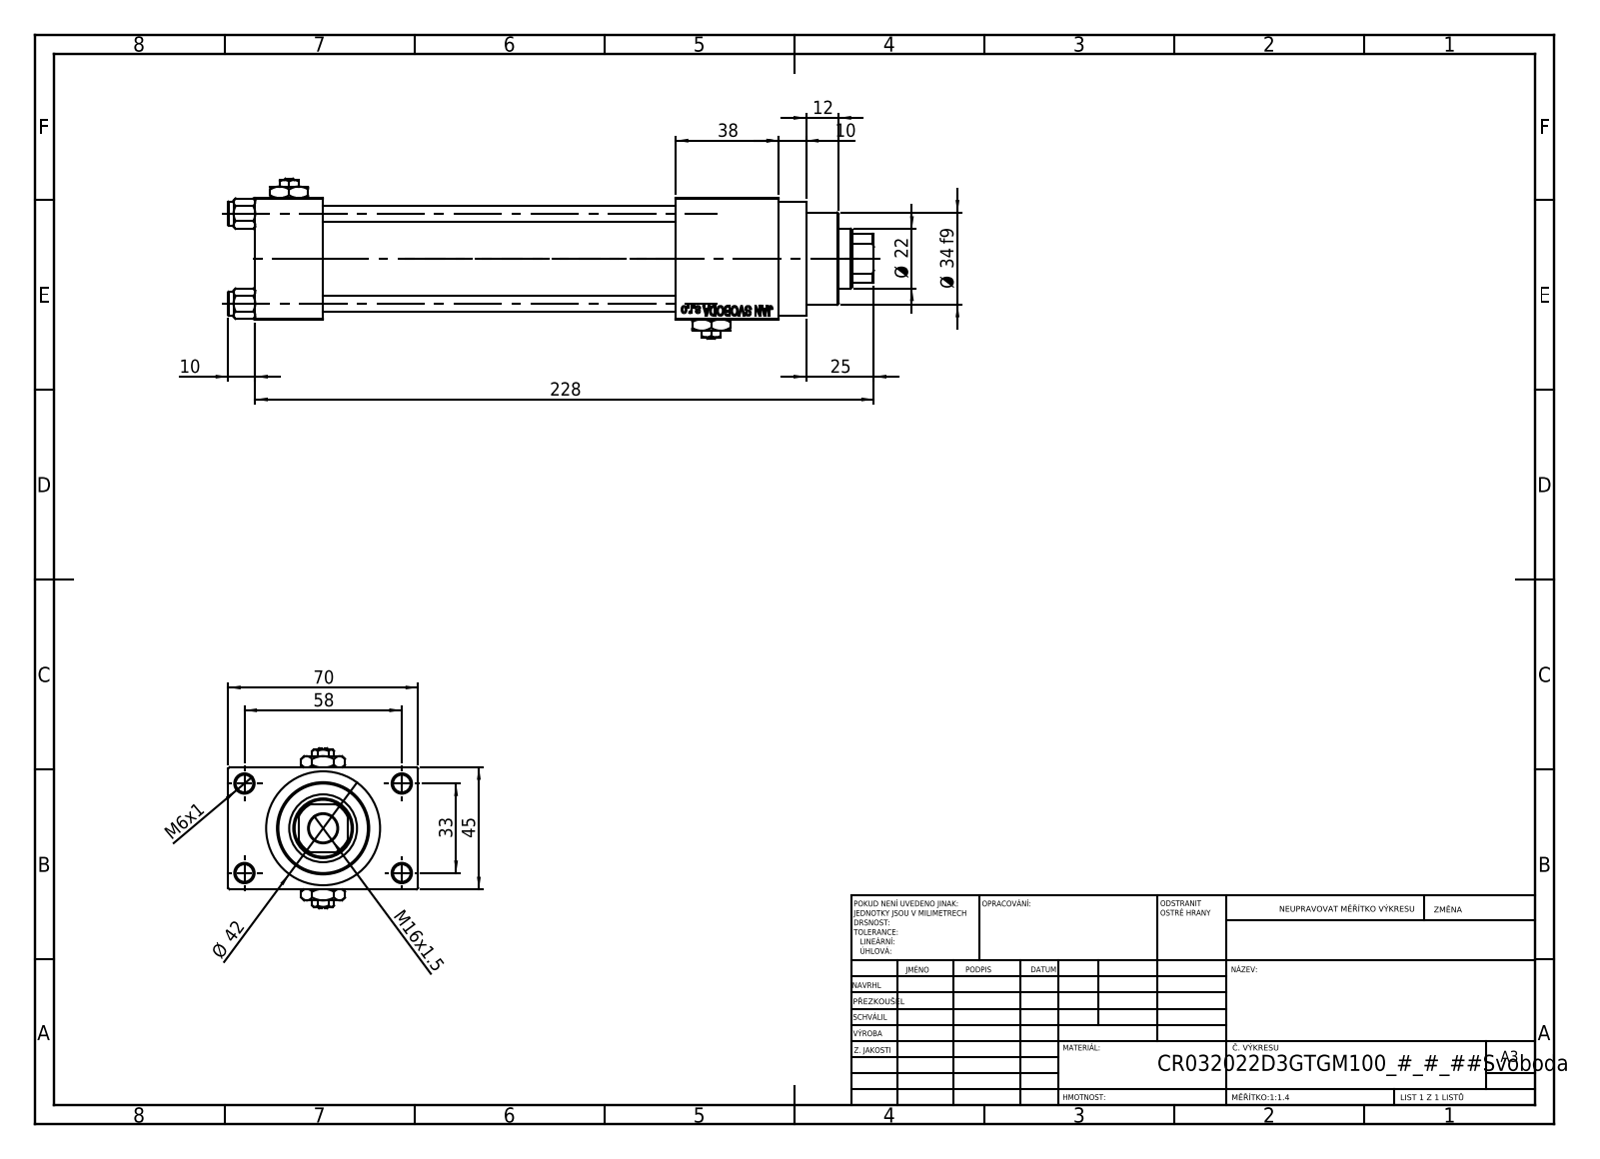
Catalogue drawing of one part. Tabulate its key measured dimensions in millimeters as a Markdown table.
| quantity | value |
| --- | --- |
| part name | Zatka_pro_OIL_PORT; V215CR_D_TYCINKA; V215_VC_A; NUT_M5_D (+2 more) |
| STEP written by | SolidWorks 2019 (CONFIG_CONTROL_DESIGN) |
| units | millimeters |
| bodies | 13 solids, 1187 faces (540 planar, 89 cylindrical, 558 other) |
| overall size | 238 × 70 × 59 |
| volume | 312 104 mm³ |
| surface area | 109 801 mm² |
| round holes (diameter × count) | 6 × 4, 6.5 × 4, 7 × 2, 13.16 × 2, 20 × 2, 10.5 × 1, 22 × 1, 24 × 1, 25 × 1, 32 × 1, 33 × 1 |
| round bosses / shafts (diameter × count) | 9 × 4, 42 × 1, 38 × 1, 34 × 1 |
| partial cylindrical surfaces (radius × count) | 10.5 × 1 |
| main face-to-face distances | 45, 25, 12.5, 57.5, 130, 155, 168, 38, 70, 193 |
| hole center spacings | 12.4, 23.48, 33.2, 33.37, 35.35, 45.6, 56.35, 33 |
